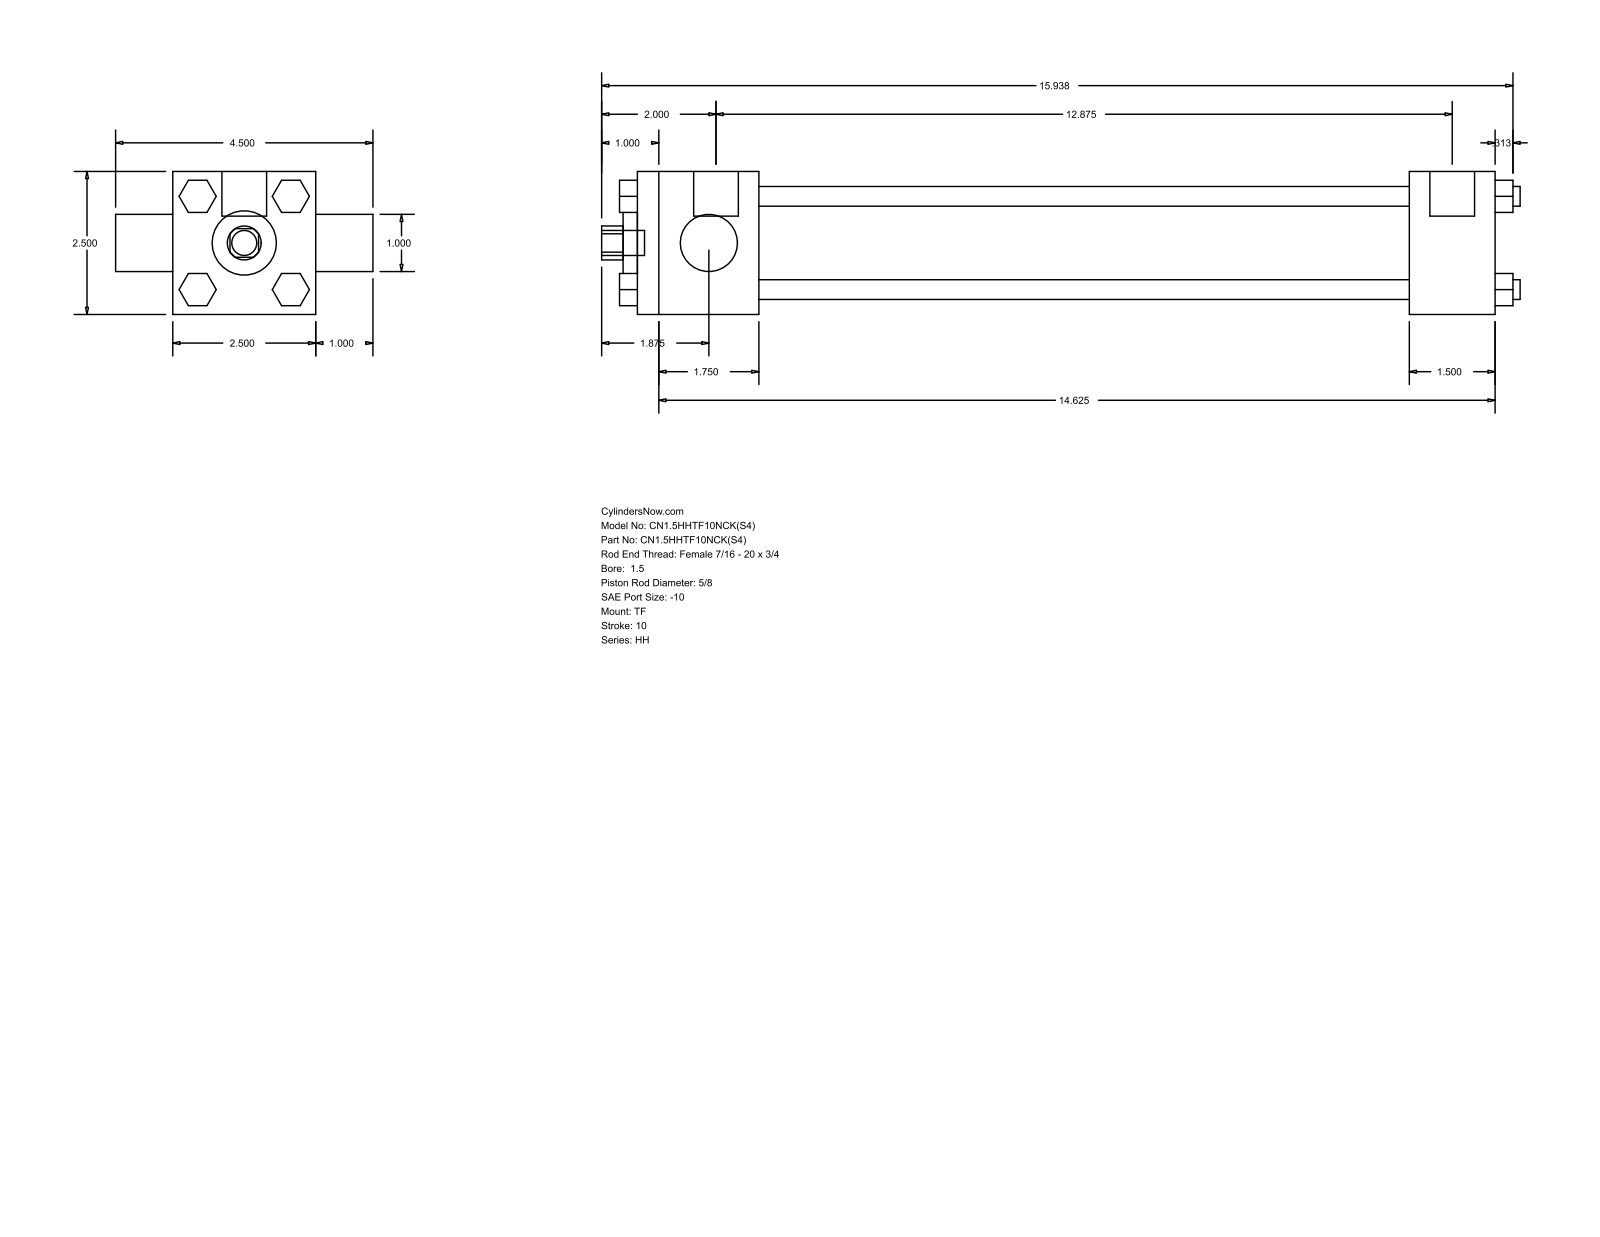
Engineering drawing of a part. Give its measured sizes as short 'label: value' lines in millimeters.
name: HH_TF__0150_0.625
written by: GSSL Pune (CONFIG_CONTROL_DESIGN)
unit: mm
bodies: 0 solids, 120 faces (92 planar, 28 cylindrical, 0 other)
size: 407.99 × 114.3 × 63.5
holes: 1× ⌀15.88, 1× ⌀25.4, 1× ⌀28.57, 1× ⌀44.45
bosses: 4× ⌀8.76, 3× ⌀5.56, 2× ⌀19.84, 1× ⌀11.11
rounds: 1× R7.54
face distances: 63.5, 381, 53.97, 327.03, 342.89, 288.92, 38.11, 25.4, 20.7, 14.29
